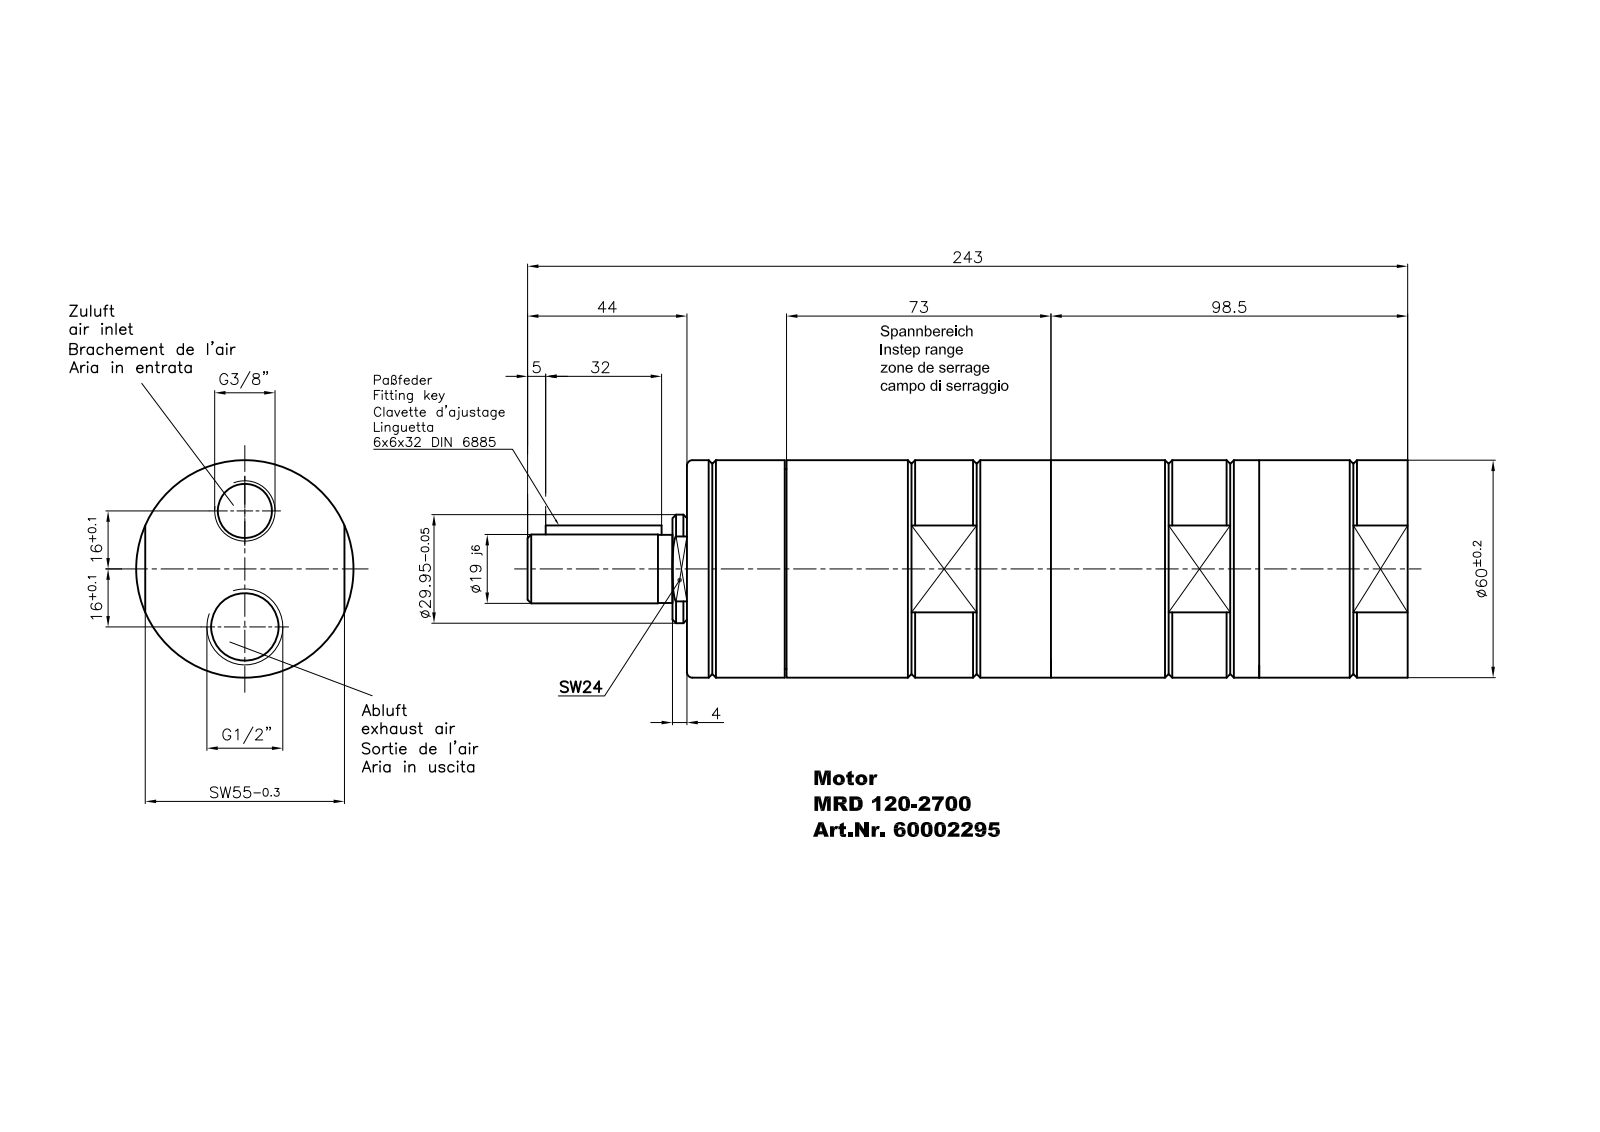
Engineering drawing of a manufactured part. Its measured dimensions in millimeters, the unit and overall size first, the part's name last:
Units: millimetres
Overall size (bounding box): 243 × 60 × 60
Round holes (diameter × count): ⌀1.55 ×1, ⌀4 ×1, ⌀5.5 ×1, ⌀35 ×1
Round bosses / shafts (diameter × count): ⌀60 ×1, ⌀58.13 ×1, ⌀29.95 ×1, ⌀19 ×1, ⌀18.8 ×1, ⌀5 ×1, ⌀3.6 ×1
Partial cylindrical surfaces — rounded edges, fillets, slot ends (radius × count): R3 ×2, R7.5 ×2, R8.5 ×1, R23.5 ×1, R26.57 ×1
Main face-to-face distances: 199, 55, 181.97, 17.03, 186, 4.03, 13, 4, 185.97, 190
Volume: 560 132 mm³ · Surface area: 51 191 mm²
Bodies: 1 solid, 121 faces (46 planar, 36 cylindrical, 39 other)
Part name (STEP PRODUCT): MRD 120-2700_60002295
STEP written by: Autodesk Inventor 2008 (CONFIG_CONTROL_DESIGN)
